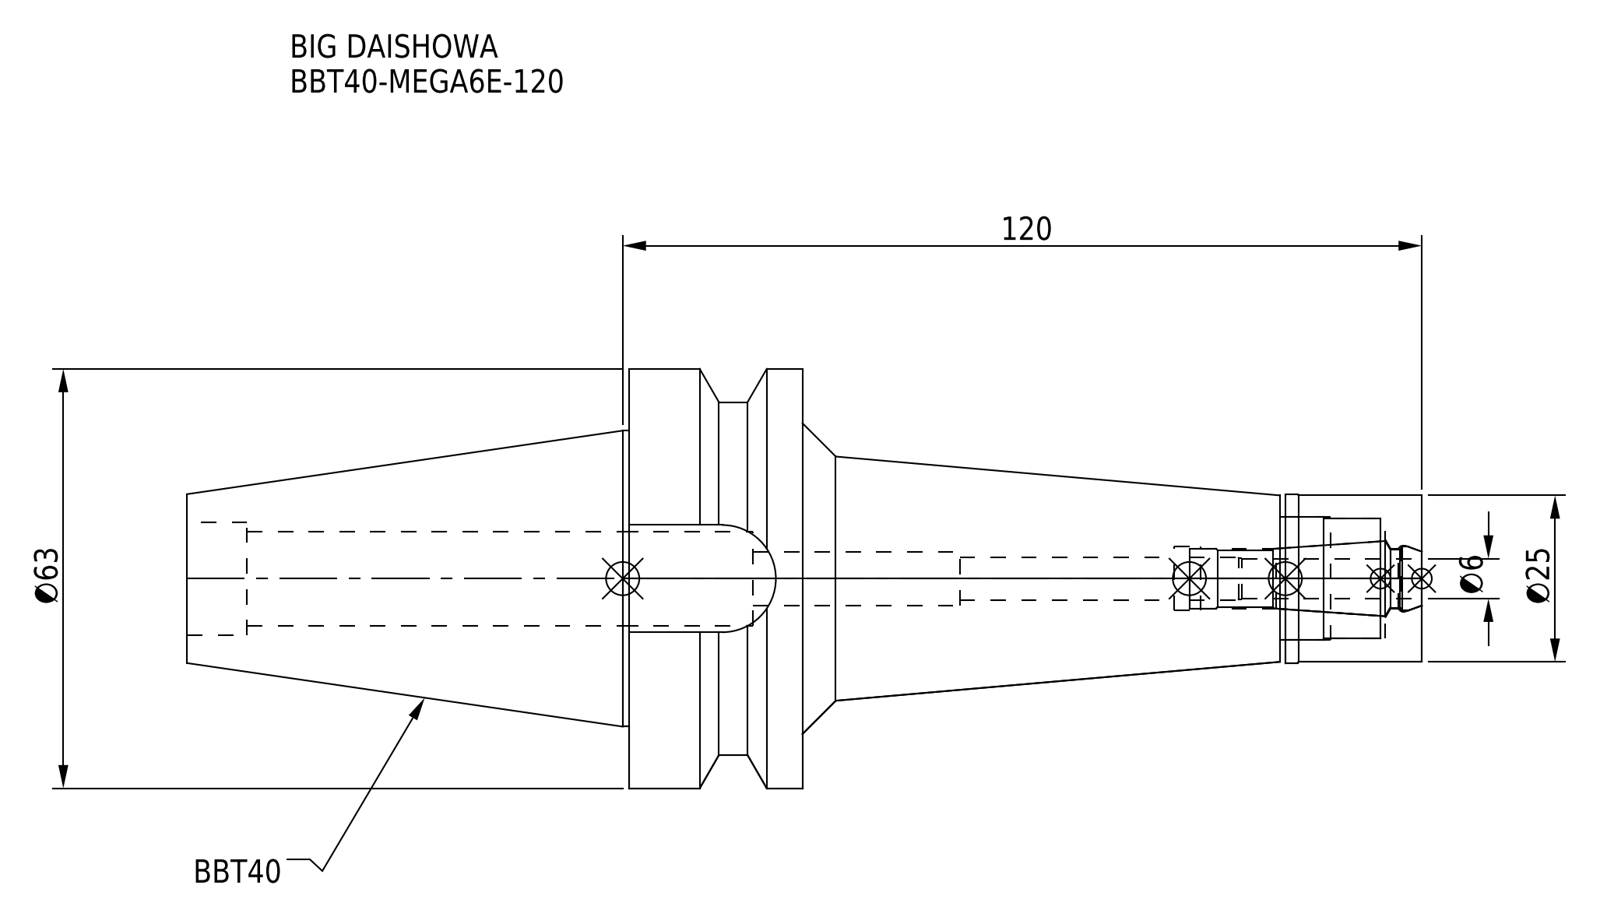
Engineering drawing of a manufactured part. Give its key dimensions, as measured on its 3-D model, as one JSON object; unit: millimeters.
{"part_name": "BBT40-MEGA6E-120-060.stp; BBT40-MEGA6E-120-060-FreeParts; MEN6_1.stp; DXF_TEMP_ASSY_ASM_4_ASM.stp (+3 more)", "step_written_by": "SolidWorks 2019 (CONFIG_CONTROL_DESIGN)", "units": "millimeters", "bodies": {"solids": 2, "faces": 81, "planar": 21, "cylindrical": 40, "other": 20}, "overall_size": [185.4, 63, 63], "volume_mm3": 183621, "surface_area_mm2": 35530, "round_holes": [[6.4, 1], [8, 1], [9, 1], [9.6, 1], [9.9, 1], [14.2, 1], [17, 1], [18, 1], [18.5, 1]], "round_bosses_or_shafts": [[63, 1], [53, 1], [44.45, 1], [25.3, 1], [25, 1]], "partial_cylinders_radius": [[8.05, 1]], "face_to_face_distances": [26, 93, 119, 45, 185.4, 92.4, 66.4, 20.5, 72.5, 98.5]}
